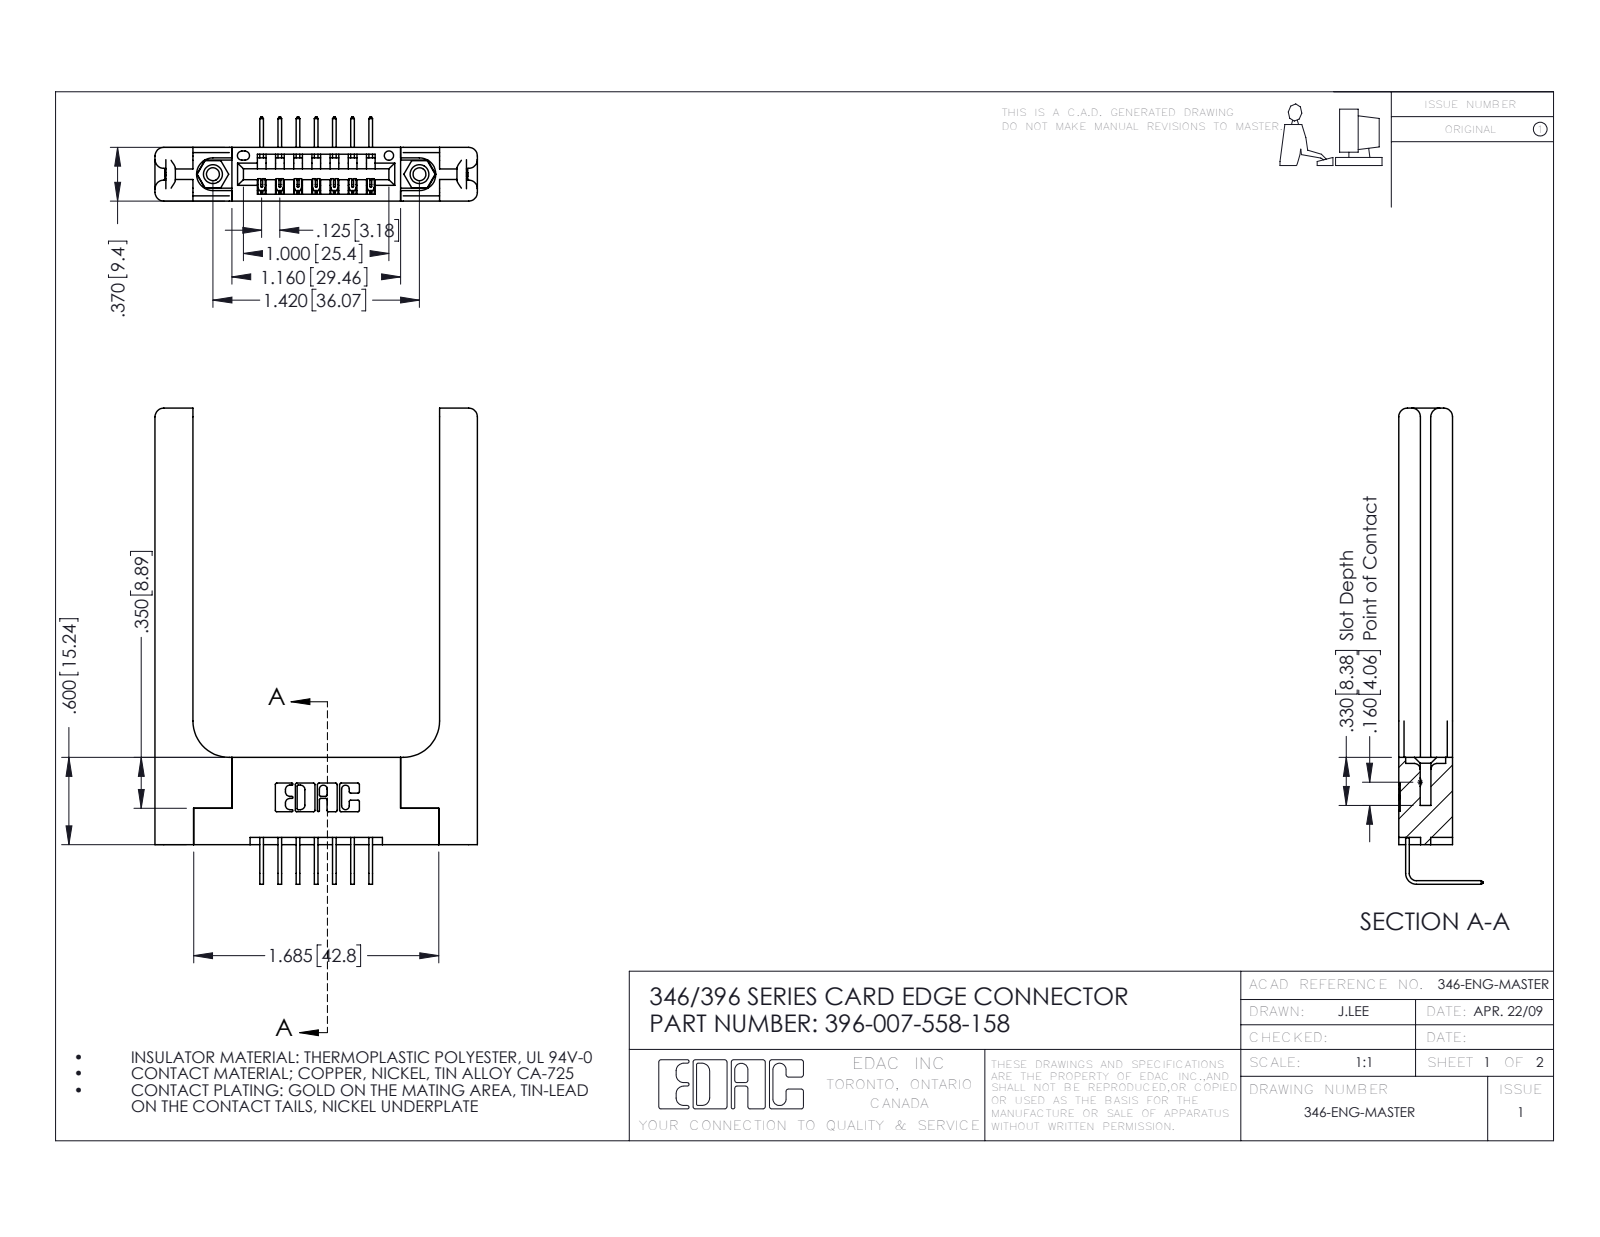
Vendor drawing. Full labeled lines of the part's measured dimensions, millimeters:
Part name (STEP PRODUCT): 396-007-558-158; 346-220-058_345-220-058; 345-292-001_558 Tail - 2; 346 Part_Flush Mounting Lugs - 0.156 Dia-TH (+1 more)
STEP written by: SolidWorks 2016 (CONFIG_CONTROL_DESIGN)
Units: millimetres
Bodies: 12 solids, 798 faces (518 planar, 220 cylindrical, 60 other)
Overall size (bounding box): 83.1 × 56.3 × 14.7
Volume: 12 700 mm³ · Surface area: 11 390 mm²
Round holes (diameter × count): ⌀2.3 ×2, ⌀3.2 ×2, ⌀4 ×2, ⌀1.6 ×1
Round bosses / shafts (diameter × count): ⌀3.9 ×2
Partial cylindrical surfaces — rounded edges, fillets, slot ends (radius × count): R0.3 ×22, R1.5 ×16, R0.2 ×14, R0.2 ×6, R0.8 ×6, R0.7 ×3, R0.8 ×2, R0.8 ×2
Main face-to-face distances: 9.4, 3.8, 5.6, 1.8, 3.8, 6.4, 8.2, 43.1, 1.2, 2.6
Hole centre spacings: 6.2, 30.9, 36.1
